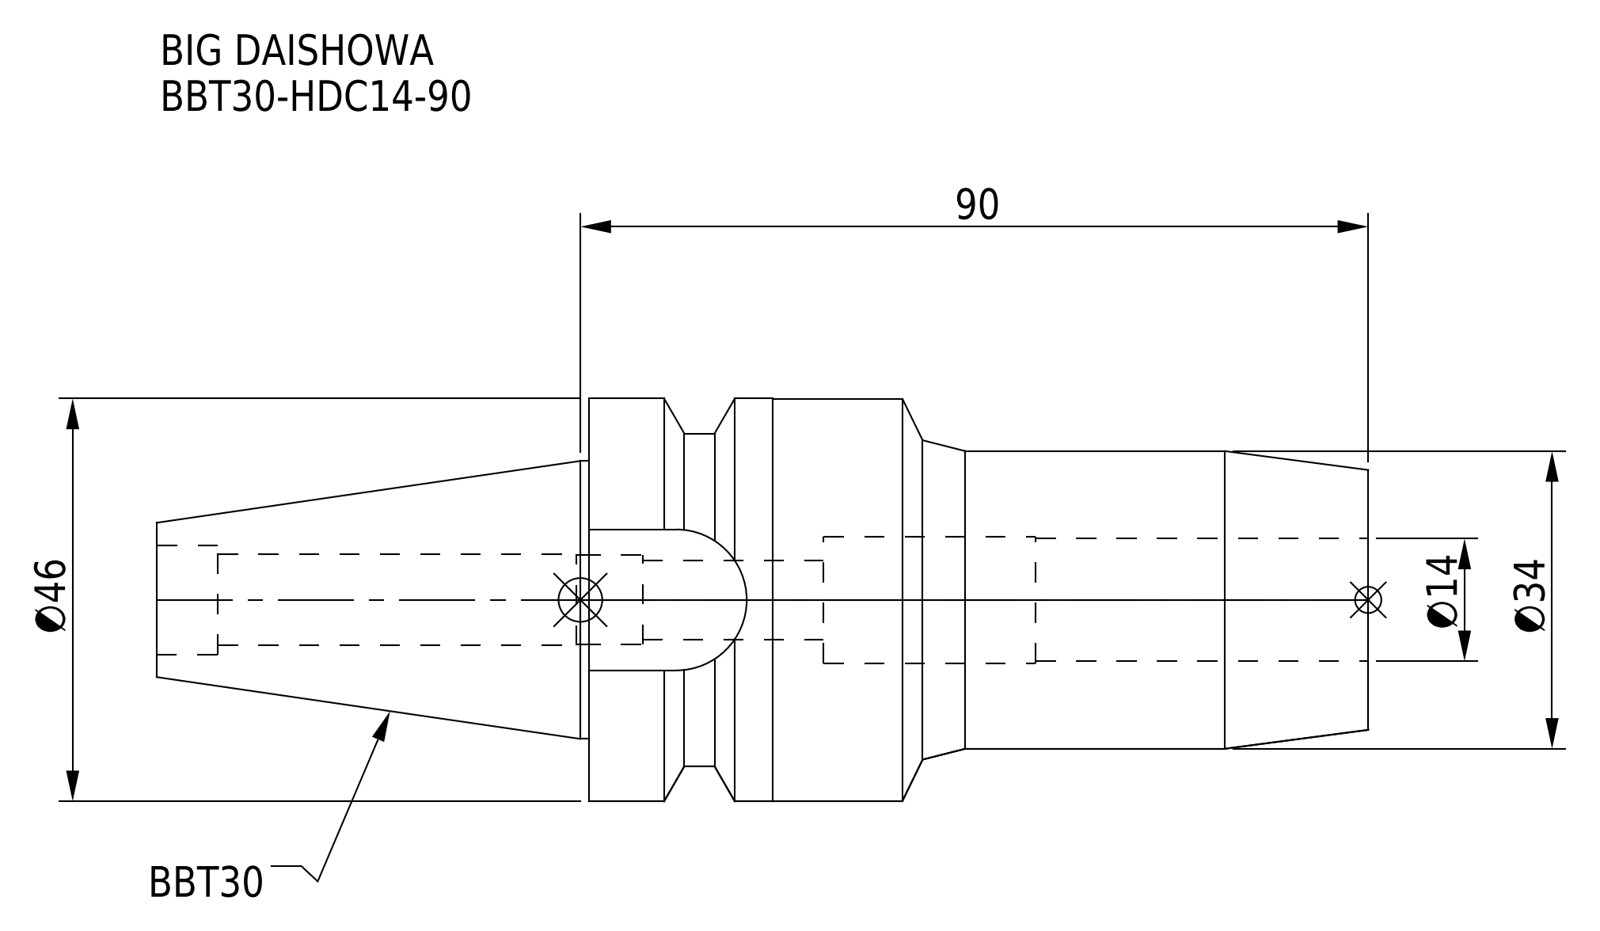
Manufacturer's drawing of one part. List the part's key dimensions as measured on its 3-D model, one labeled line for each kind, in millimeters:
Part name (STEP PRODUCT): BBT30-HDC14-90
STEP written by: CREO PARAMETRIC BY PTC INC, 2016380 (AUTOMOTIVE_DESIGN)
Units: millimetres
Bodies: 1 solid, 55 faces (15 planar, 28 cylindrical, 12 other)
Overall size (bounding box): 138.4 × 46 × 46
Volume: 110 020 mm³ · Surface area: 22 565 mm²
Round holes (diameter × count): ⌀9 ×1, ⌀10.2 ×1, ⌀10.4 ×1, ⌀12.5 ×1, ⌀14 ×1, ⌀14.5 ×1
Round bosses / shafts (diameter × count): ⌀46 ×1, ⌀45.9 ×1, ⌀34 ×1, ⌀31.75 ×1
Partial cylindrical surfaces — rounded edges, fillets, slot ends (radius × count): R8.05 ×1, R19 ×1
Main face-to-face distances: 89, 32.6, 138.4, 49.4, 62.2, 26.8, 76.2, 16.1, 131.4, 69.2
